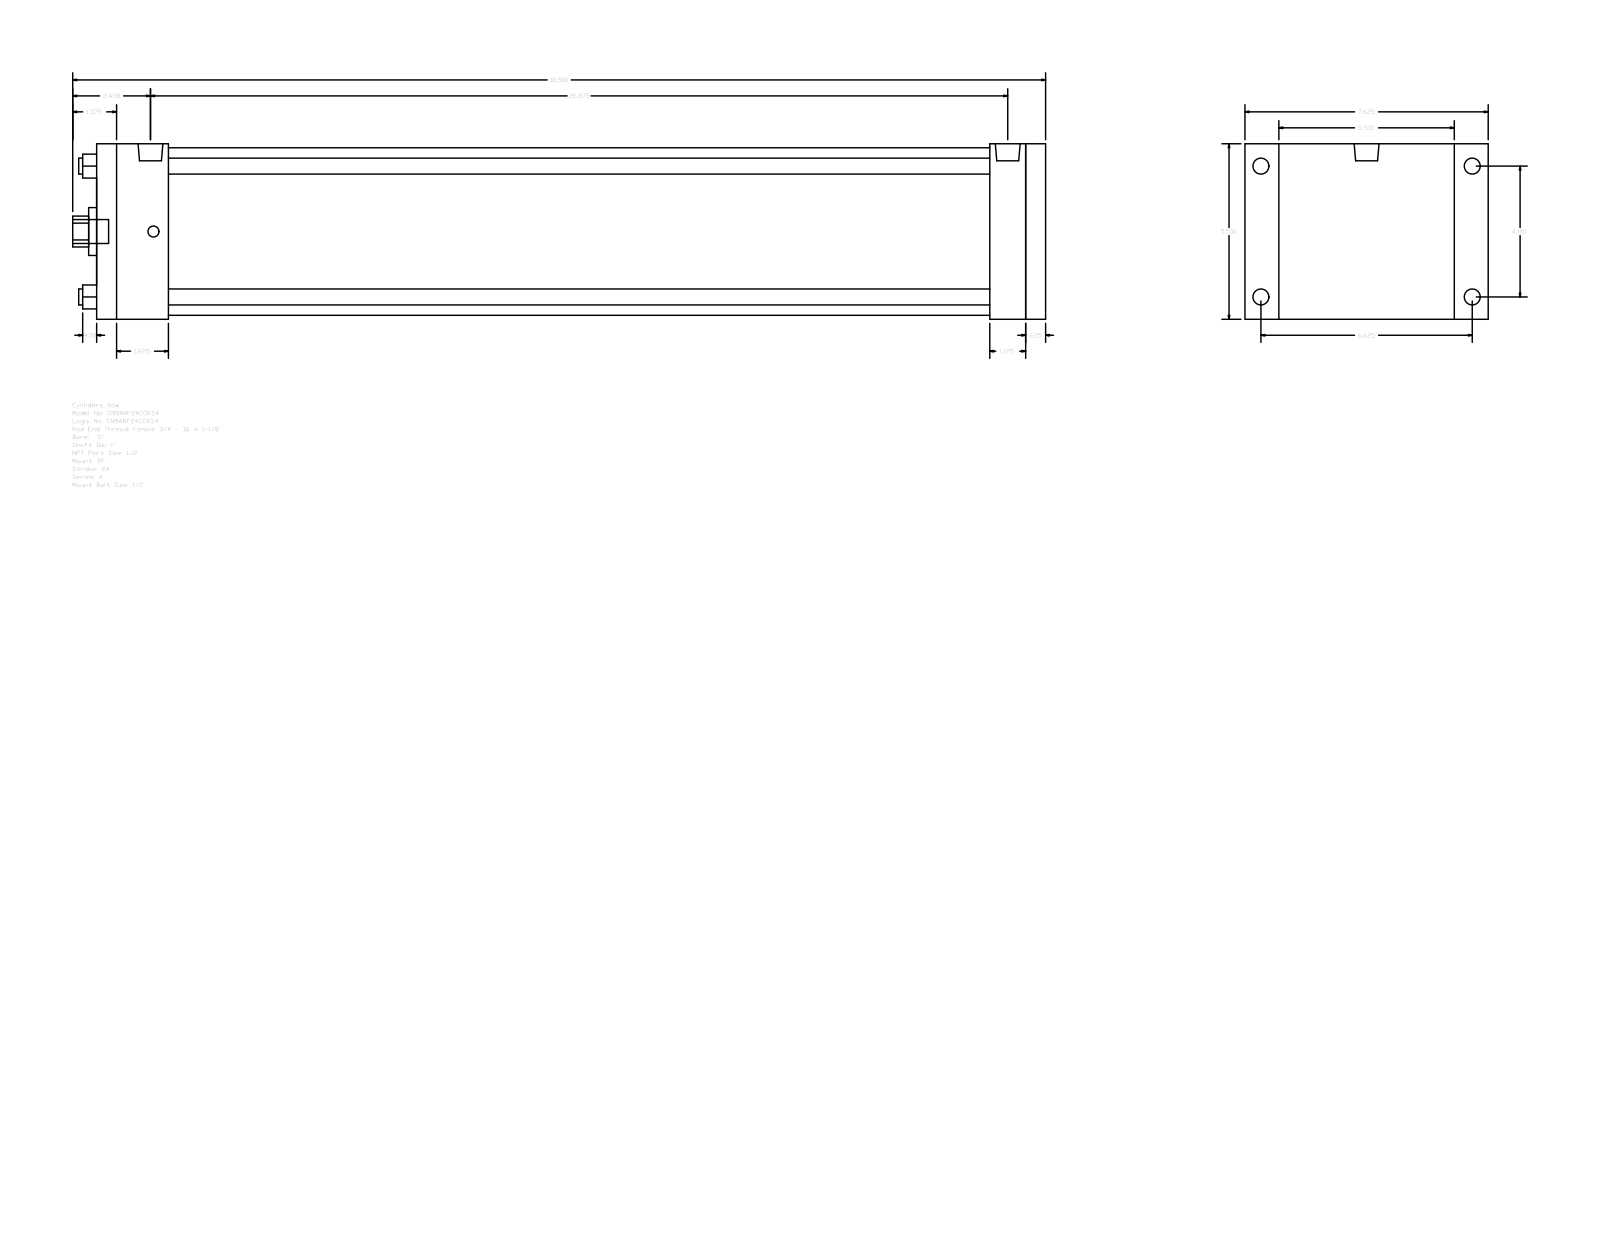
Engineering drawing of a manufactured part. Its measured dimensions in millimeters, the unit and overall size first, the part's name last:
Units: millimetres
Overall size (bounding box): 774.7 × 193.68 × 139.7
Round holes (diameter × count): ⌀12.7 ×4, ⌀25.4 ×1, ⌀38.1 ×1, ⌀133.35 ×1
Round bosses / shafts (diameter × count): ⌀12.7 ×4, ⌀8.73 ×4, ⌀19.77 ×2, ⌀19.05 ×1
Partial cylindrical surfaces — rounded edges, fillets, slot ends (radius × count): R12.29 ×1
Main face-to-face distances: 139.7, 755.65, 15.87, 739.78, 57.15, 682.63, 698.5, 711.2, 654.05, 28.58
Hole centre spacings: 73.64, 104.14, 147.28
Bodies: 0 solids, 92 faces (64 planar, 28 cylindrical, 0 other)
Part name (STEP PRODUCT): A_RF__0500_1
STEP written by: GSSL Pune (CONFIG_CONTROL_DESIGN)
